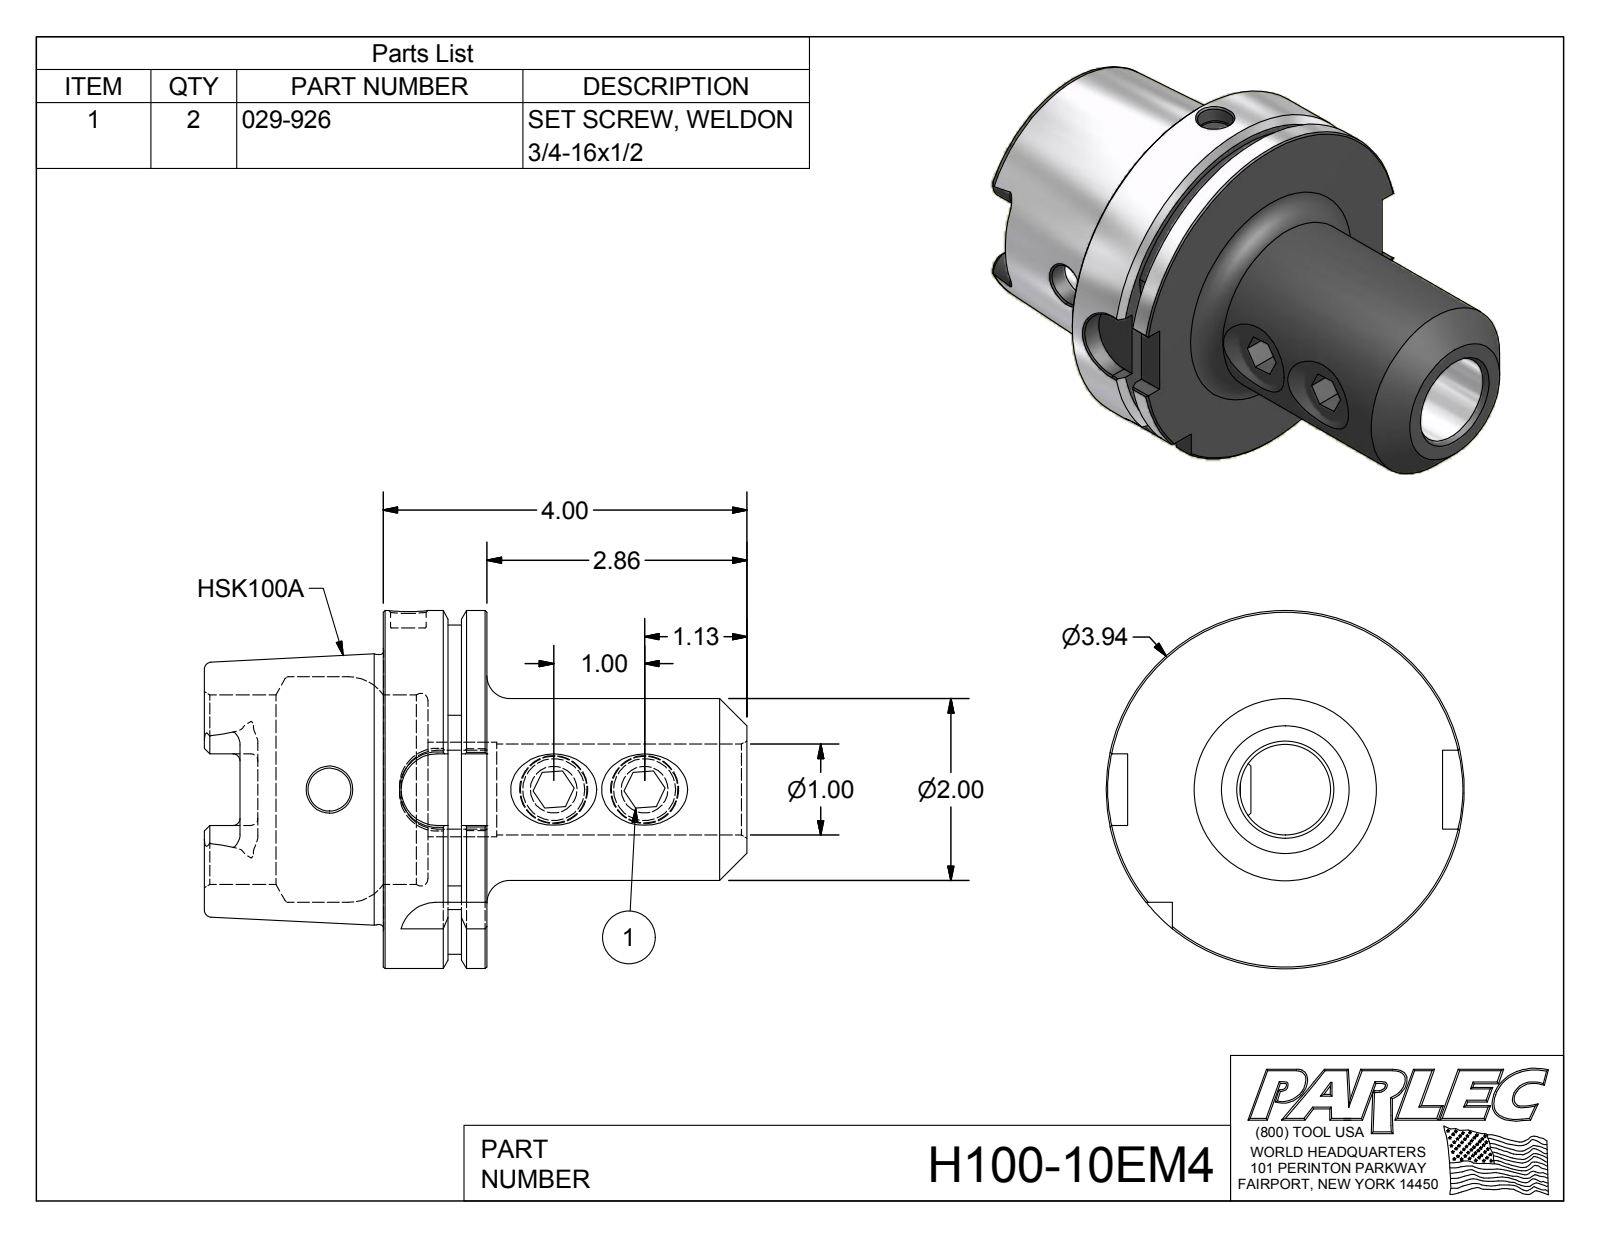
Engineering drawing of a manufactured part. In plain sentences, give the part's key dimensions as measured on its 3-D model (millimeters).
The part is named "H100-10EM4; 029-926". Its 3-D file was written by "Autodesk Inventor 2012 (AUTOMOTIVE_DESIGN)". It is 3 solids with 146 faces: 59 planar, 35 cylindrical and 52 other. Overall it measures 151.6 by 100 by 100 millimeters. Its volume is 356 900 cubic millimeters and its surface area 68 840 square millimeters. Round holes: 2 of diameter 17.3, 1 of diameter 10, 1 of diameter 12, 1 of diameter 25.4, 1 of diameter 26.4, 1 of diameter 53, 1 of diameter 63. Round bosses or shafts: 2 of diameter 19.1, 1 of diameter 100, 1 of diameter 75.4, 1 of diameter 50.8. Partial cylindrical surfaces (rounded edges, fillets, slot ends): 6 of radius 2, 4 of radius 4.9, 4 of radius 10, 1 of radius 46. The main face-to-face distances are 29, 12.5, 16.5, 50, 62.5, 79, 71.9, 21.9, 9.4, 7.1. The hole center spacings are 25.4, 62.6, 88.
